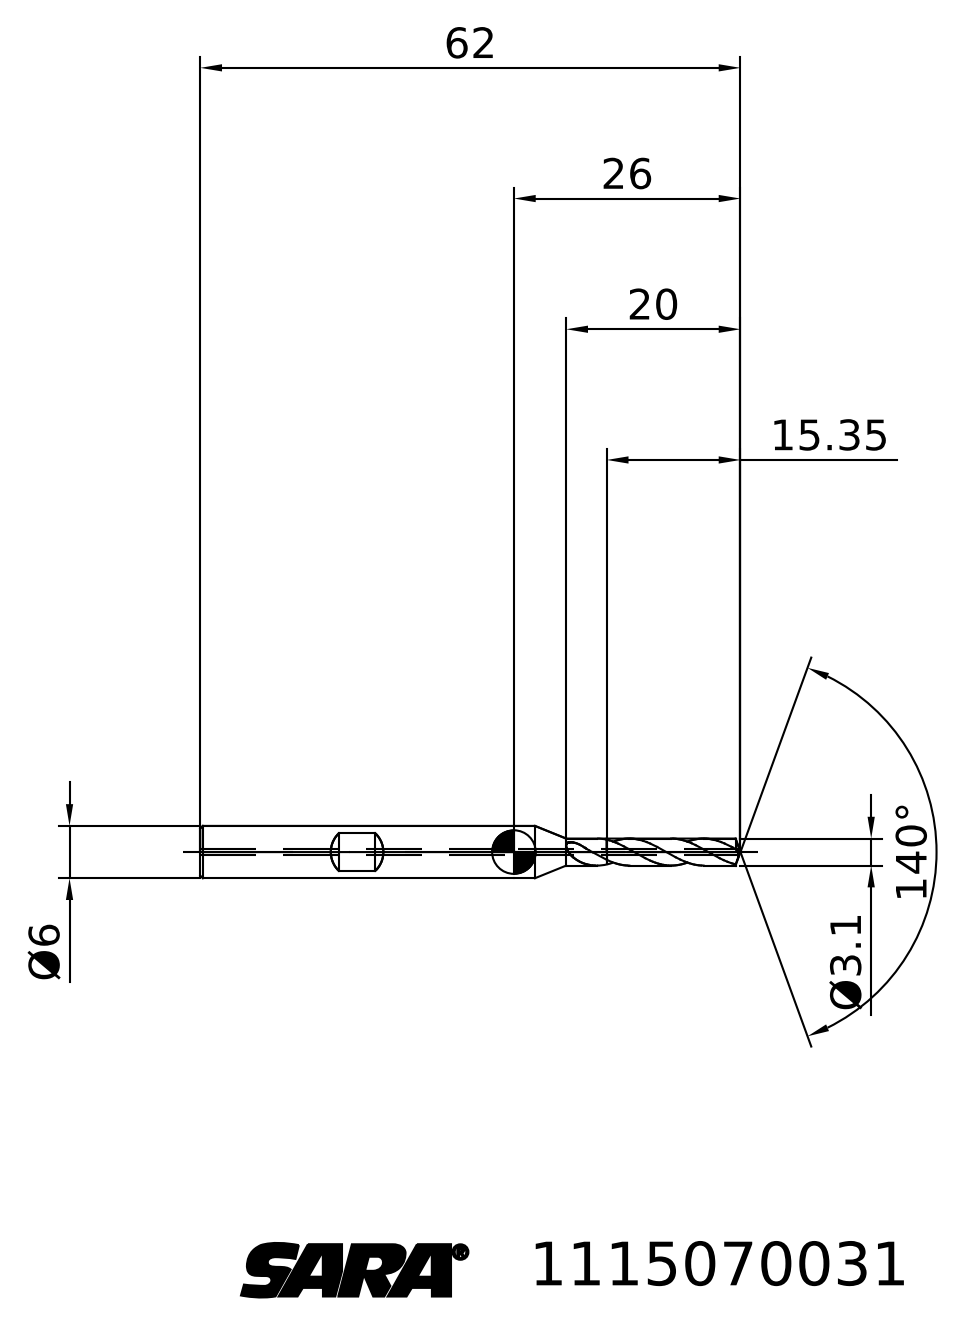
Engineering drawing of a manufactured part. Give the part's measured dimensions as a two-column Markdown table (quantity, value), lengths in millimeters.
| quantity | value |
| --- | --- |
| STEP written by | TDM (AUTOMOTIVE_DESIGN) |
| units | millimeters |
| bodies | 2 solids, 29 faces (6 planar, 0 cylindrical, 23 other) |
| overall size | 62 × 7.4 × 6 |
| volume | 1 232 mm³ |
| surface area | 1 027 mm² |
| main face-to-face distances | 46.65 |
